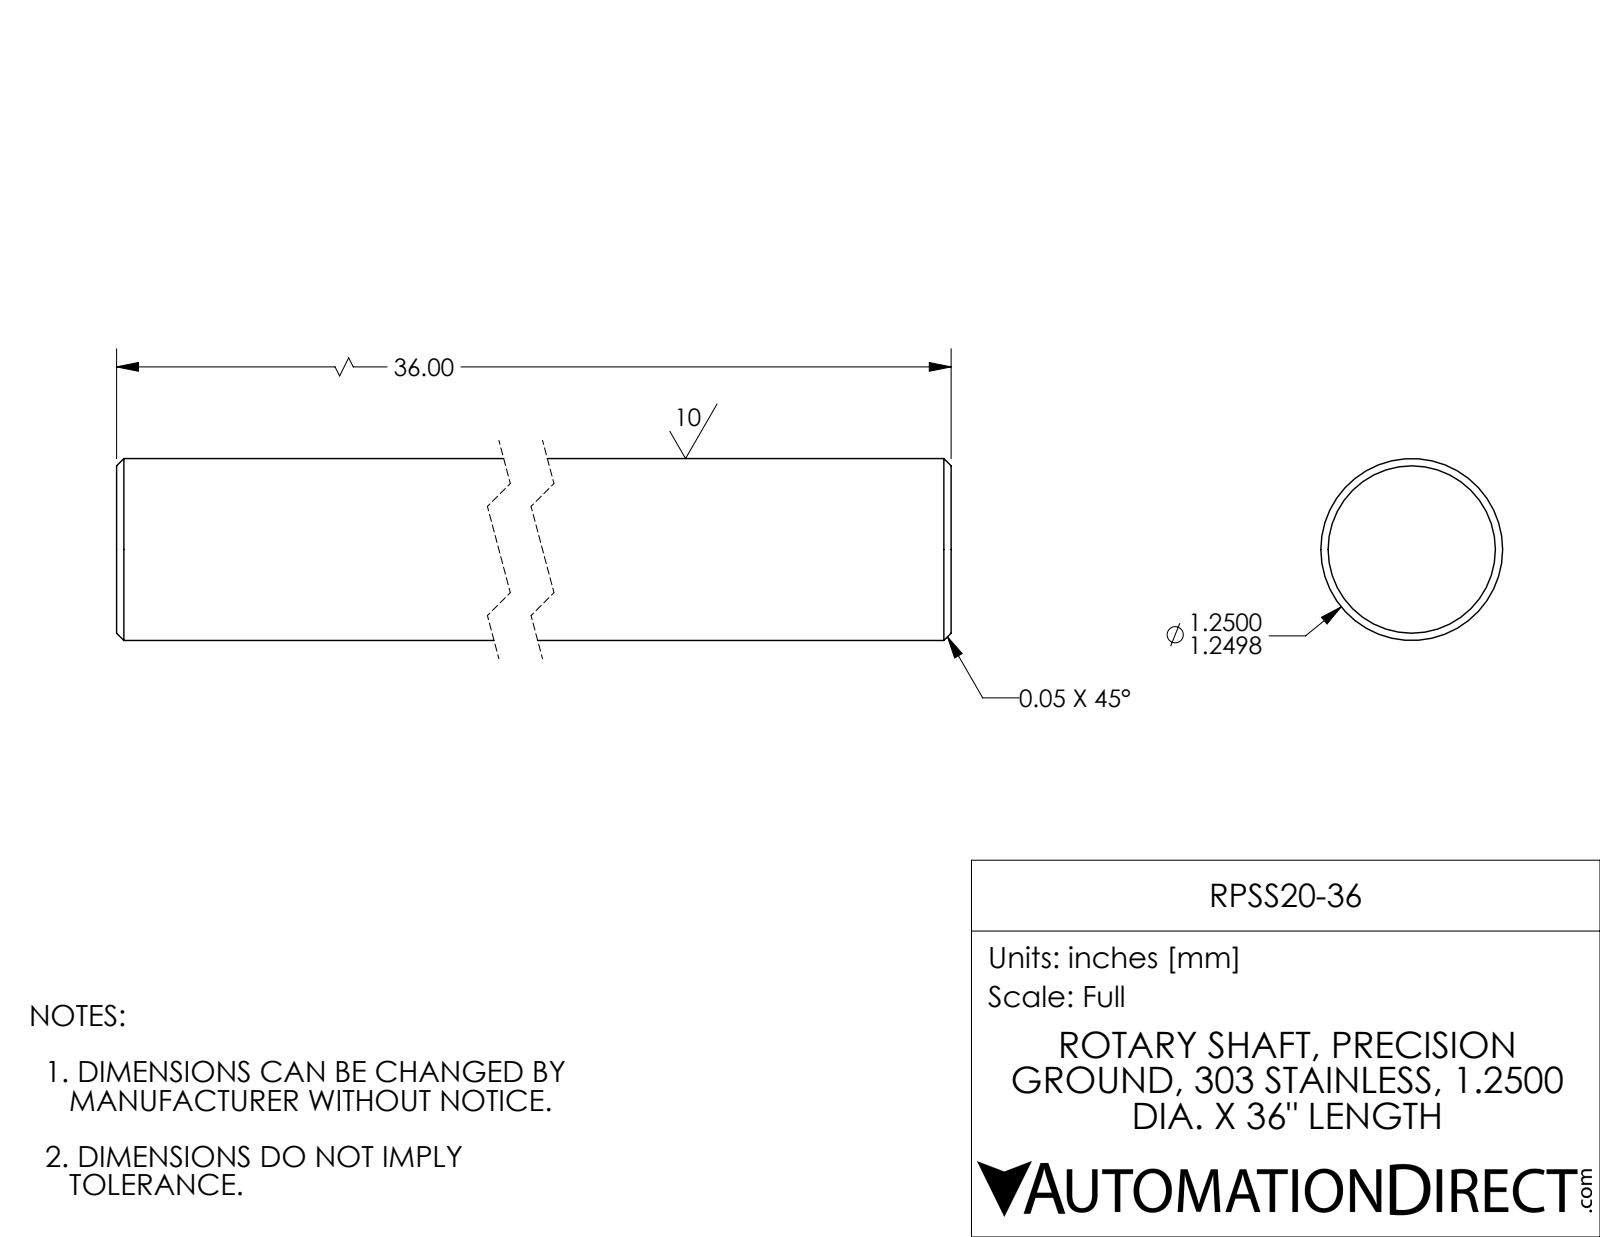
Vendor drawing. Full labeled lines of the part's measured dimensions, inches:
Part name (STEP PRODUCT): RPSS20-36
STEP written by: SolidWorks 2017 (AUTOMOTIVE_DESIGN)
Units: inches
Bodies: 1 solid, 8 faces (2 planar, 2 cylindrical, 4 other)
Overall size (bounding box): 36 × 1.25 × 1.25
Volume: 44.17 in³ · Surface area: 143.6 in²
Round bosses / shafts (diameter × count): ⌀1.25 ×1
Main face-to-face distances: 36
